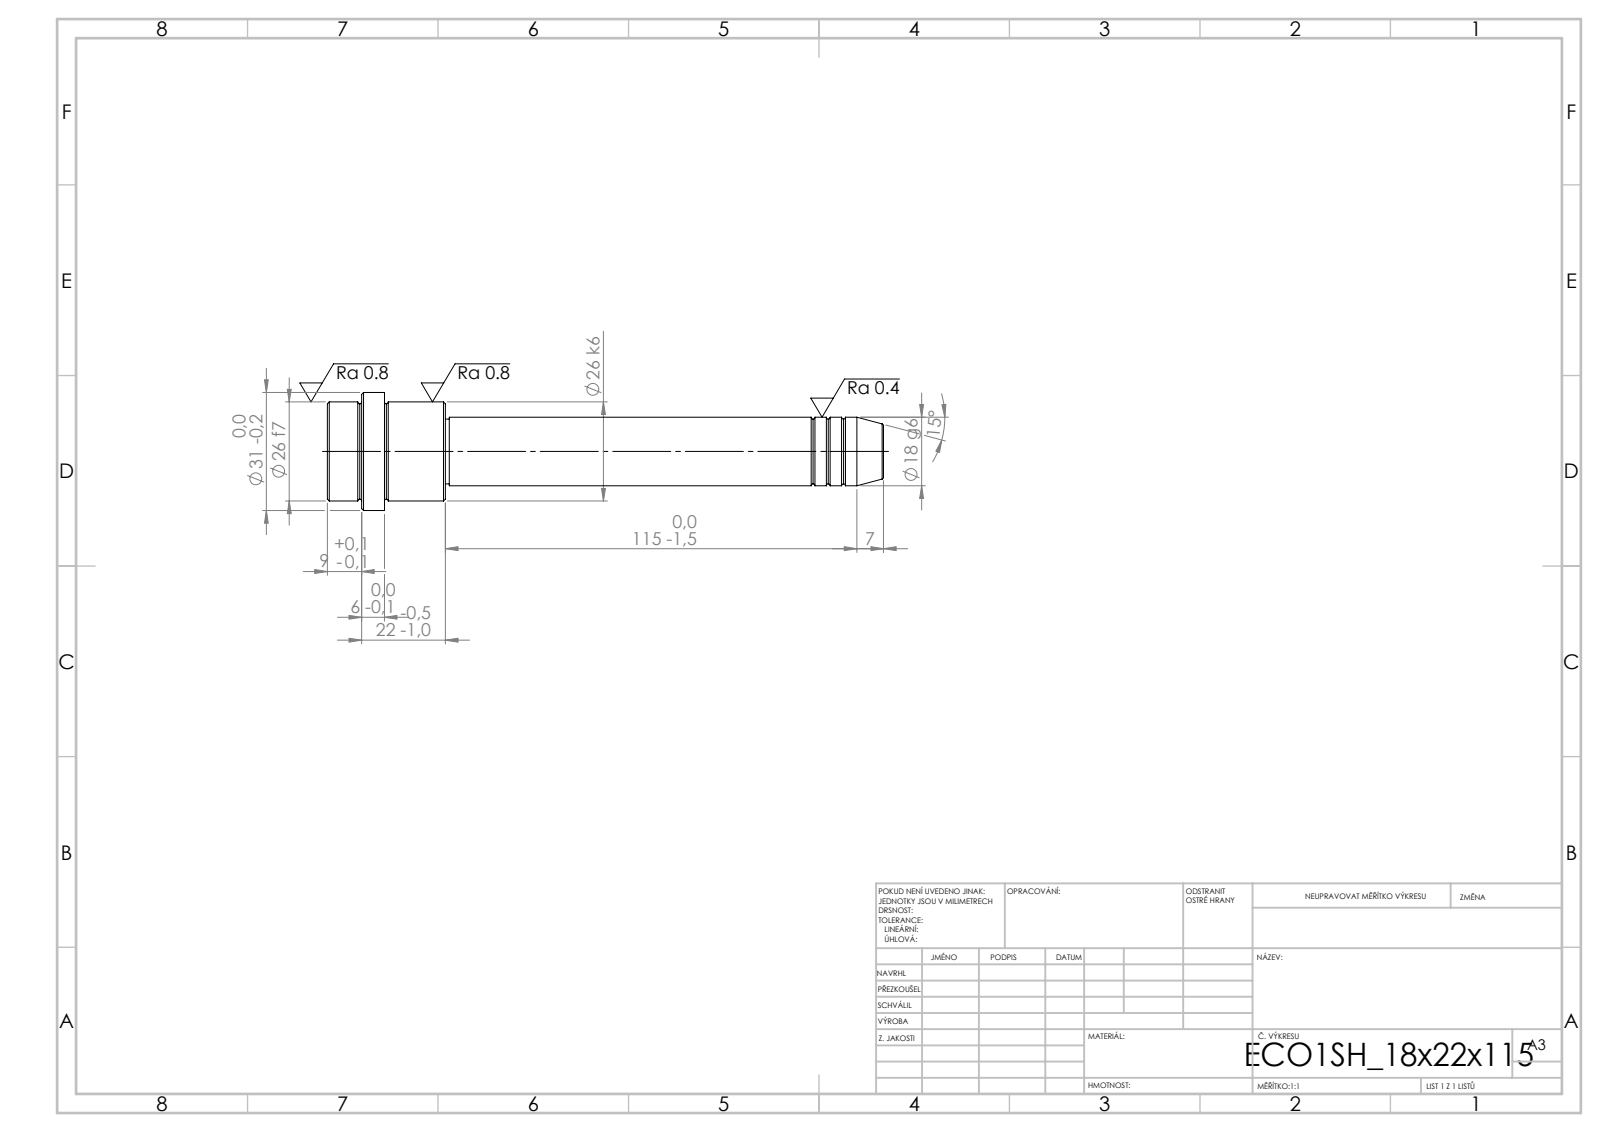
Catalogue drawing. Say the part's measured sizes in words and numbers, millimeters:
Its 3-D file was written by "SolidWorks 2019 (CONFIG_CONTROL_DESIGN)". It is 1 solid with 52 faces: 6 planar, 16 cylindrical and 30 other. Overall it measures 146 by 31 by 31 millimeters. Its volume is 46 531 cubic millimeters and its surface area 10 659 square millimeters. Round bosses or shafts: 1 of diameter 31, 1 of diameter 26, 1 of diameter 18, 1 of diameter 17. The main face-to-face distances are 31, 16, 15, 22, 6, 9, 115, 131, 137, 146.
